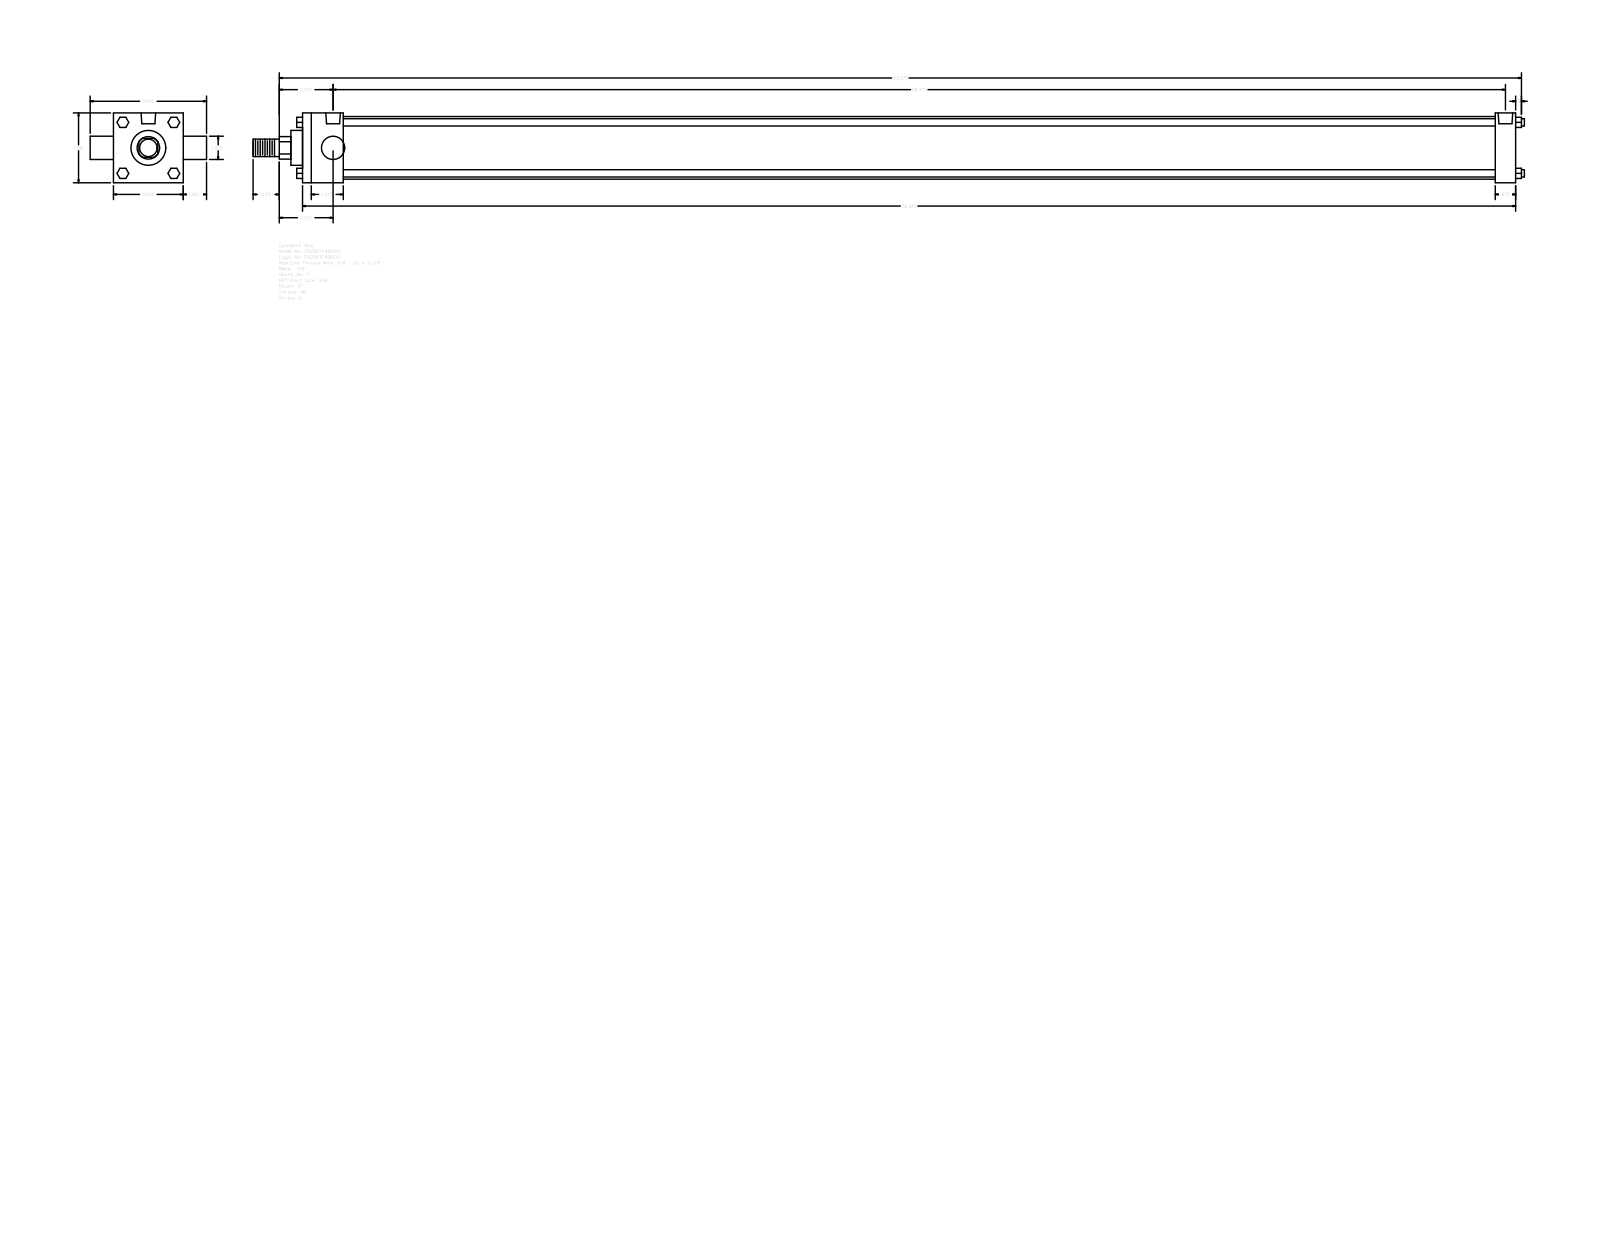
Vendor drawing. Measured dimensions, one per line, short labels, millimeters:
name: A_TF__0250_1
written by: GSSL Pune (CONFIG_CONTROL_DESIGN)
unit: mm
bodies: 0 solids, 120 faces (92 planar, 28 cylindrical, 0 other)
size: 1387.47 × 127 × 76.2
holes: 3× ⌀5.56, 2× ⌀15.93
bosses: 4× ⌀7.94, 2× ⌀25.4, 1× ⌀68.33, 1× ⌀38.1, 1× ⌀19.05
rounds: 1× R12.29
face distances: 76.2, 1323.98, 44.45, 1301.75, 1257.3, 1279.53, 22.23, 25.4, 101.6, 12.7
hole spacings: 2.38, 1281.9, 1279.52, 1284.28
